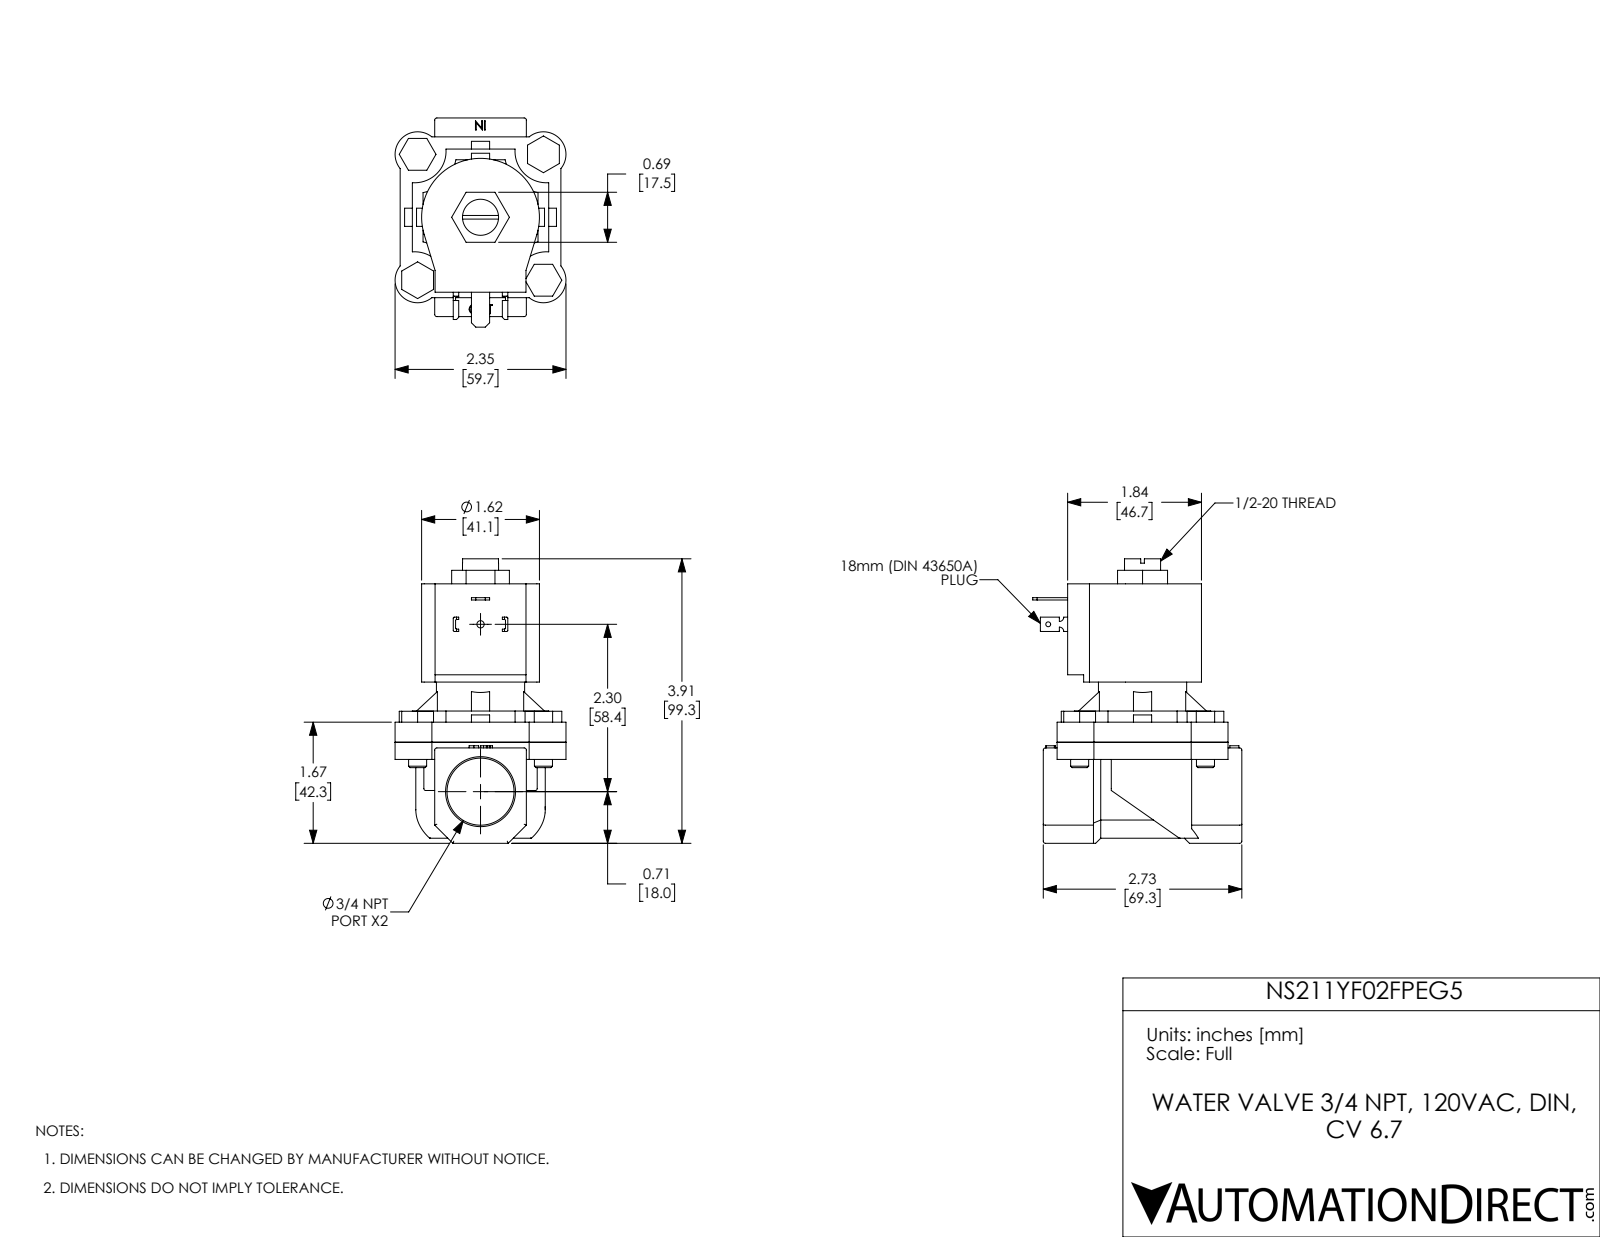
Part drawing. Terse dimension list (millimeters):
name: NS211YF02FPEG5
written by: SolidWorks 2017 (AUTOMOTIVE_DESIGN)
unit: mm
bodies: 11 solids, 387 faces (241 planar, 113 cylindrical, 33 other)
size: 99.3 × 73 × 59.7
volume: 163 800 mm³; area: 44 100 mm²
holes: 4× ⌀6.4, 1× ⌀1.7, 1× ⌀2.5, 1× ⌀12.6, 1× ⌀13, 1× ⌀23.4, 1× ⌀29.3
bosses: 4× ⌀6.3, 1× ⌀30.8
rounds: 15× R0.8, 8× R0.4, 4× R7.9, 4× R11, 4× R14.7, 2× R1.5, 1× R20.6, 1× R22.6
face distances: 7, 55.3, 48.3, 6, 13, 61.3, 27, 21, 14, 34.3
hole spacings: 31.1, 43.9, 62.1, 58.4
